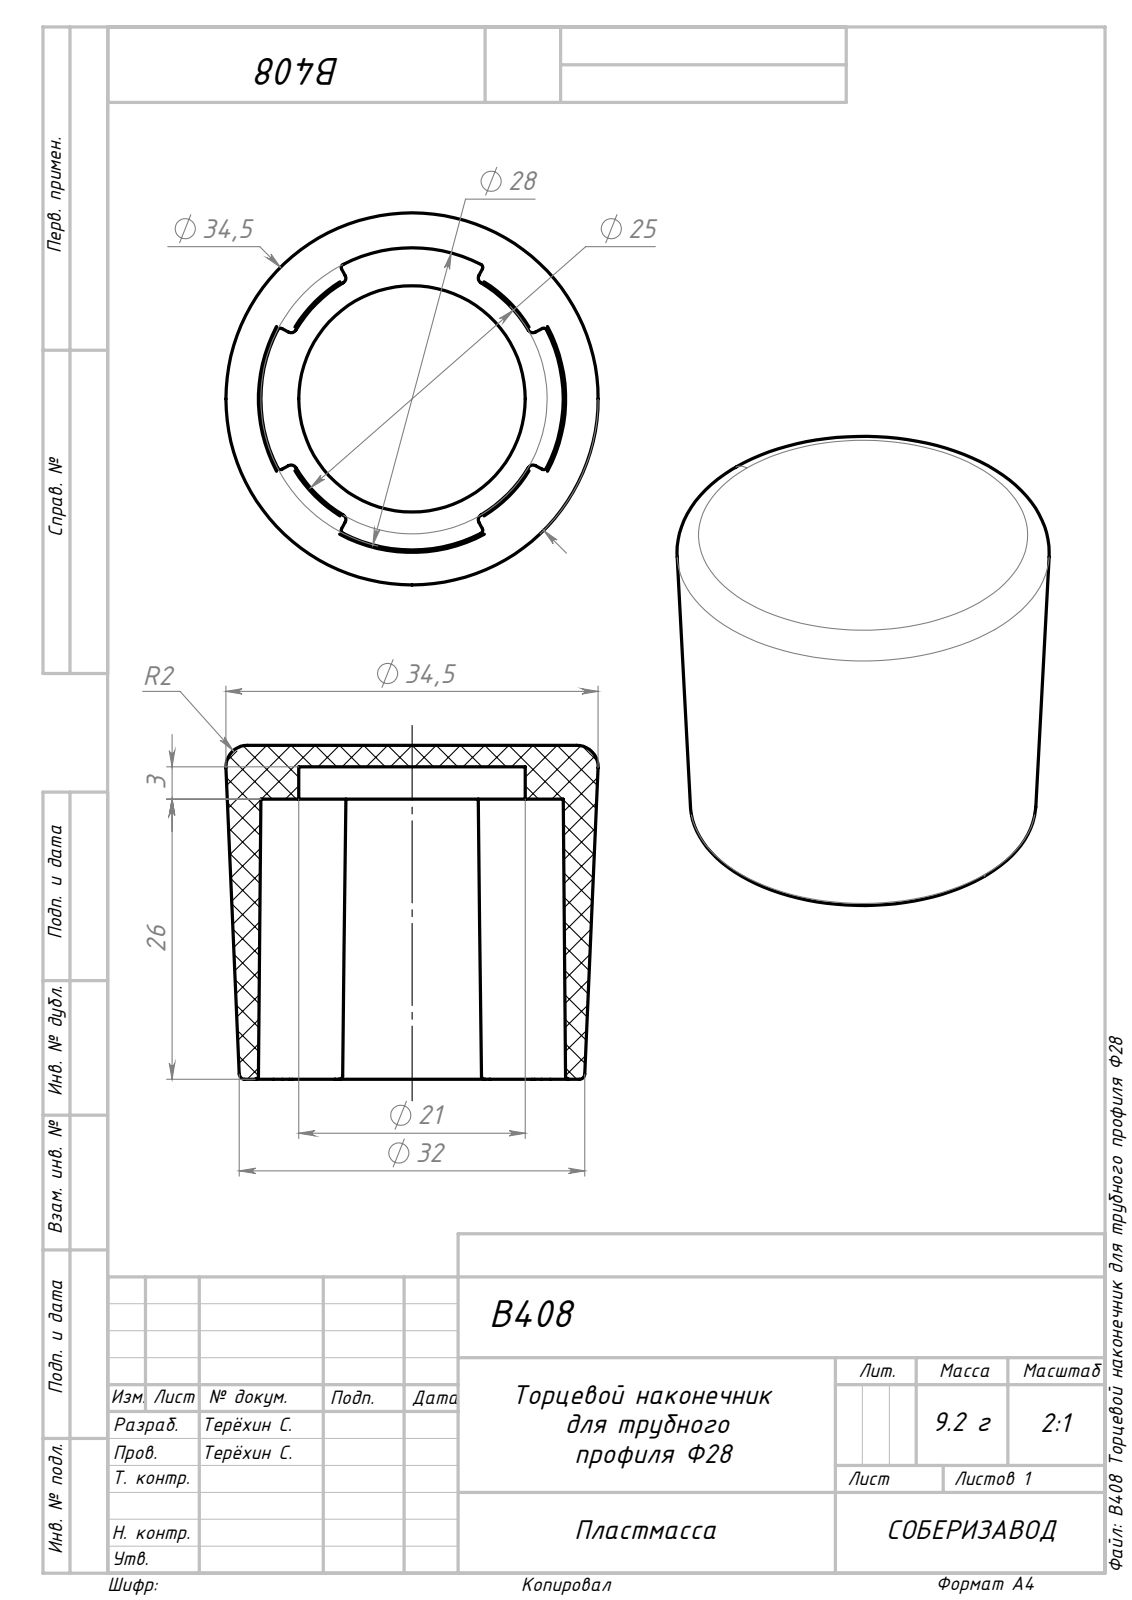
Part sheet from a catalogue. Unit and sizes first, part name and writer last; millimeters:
Units: millimetres
Overall size (bounding box): 34.53 × 34.53 × 31
Round holes (diameter × count): ⌀21 ×1
Partial cylindrical surfaces — rounded edges, fillets, slot ends (radius × count): R0.3 ×8
Main face-to-face distances: 2, 3, 5, 26, 29, 31
Volume: 10 796 mm³ · Surface area: 7 502 mm²
Bodies: 1 solid, 81 faces (12 planar, 10 cylindrical, 59 other)
Part name (STEP PRODUCT): B408 Торцевой наконечник для трубного профиля Ф28
STEP written by: SolidWorks 2022 (AUTOMOTIVE_DESIGN)
